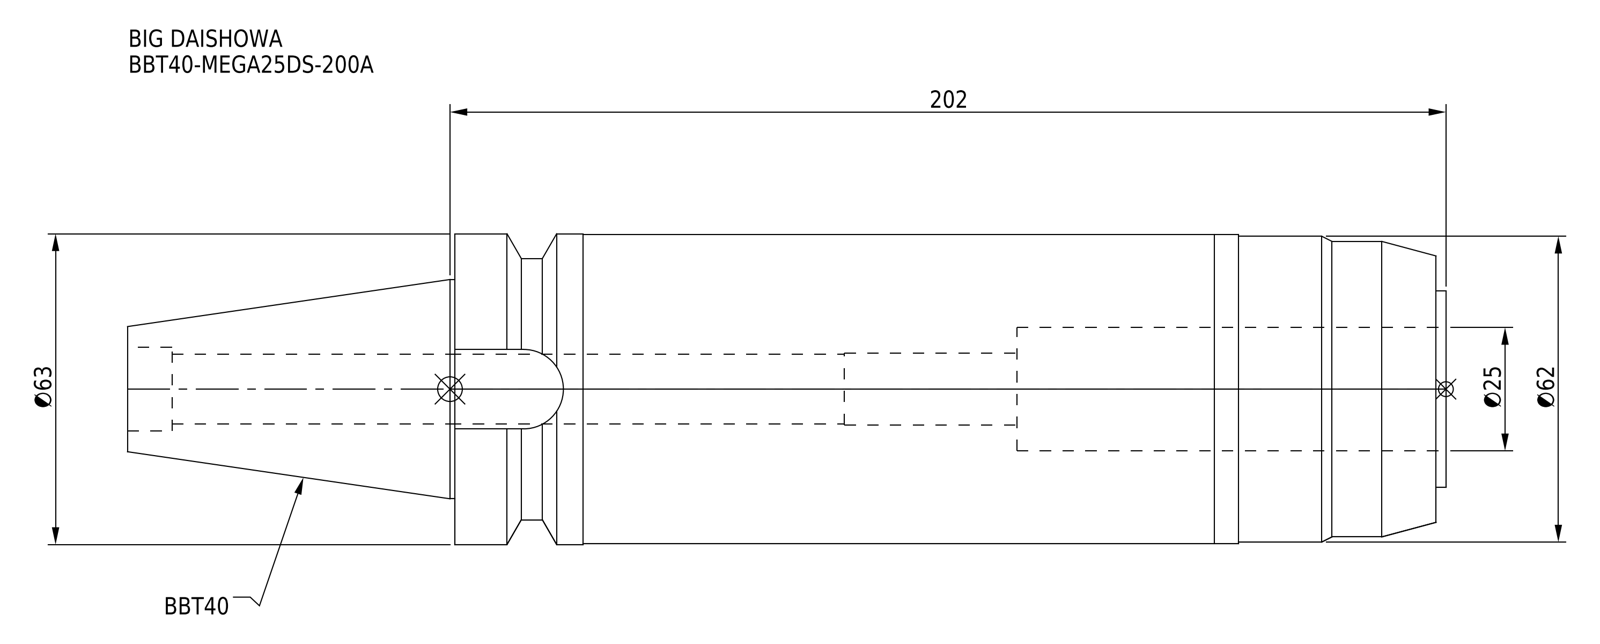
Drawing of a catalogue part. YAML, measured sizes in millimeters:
part_name: "BBT40-MEGA25DS-200A"
step_written_by: "CREO PARAMETRIC BY PTC INC, 2016380 (AUTOMOTIVE_DESIGN)"
units: millimeters
bodies: {solids: 1, faces: 53, planar: 15, cylindrical: 28, other: 10}
overall_size: [267.4, 63, 63]
volume: 589957
surface_area: 66869
round_holes:
  - {diameter: 14.2, count: 1}
  - {diameter: 14.5, count: 1}
  - {diameter: 17, count: 1}
  - {diameter: 25, count: 1}
round_bosses_or_shafts:
  - {diameter: 63, count: 1}
  - {diameter: 62.7, count: 1}
  - {diameter: 62, count: 1}
  - {diameter: 59.9, count: 1}
  - {diameter: 53, count: 1}
  - {diameter: 44.45, count: 1}
  - {diameter: 39.9, count: 1}
partial_cylinders:
  - {radius: 8.05, count: 1}
face_to_face_distances: [199, 2, 201, 45, 87, 85, 114, 267.4, 265.4, 180.4]
